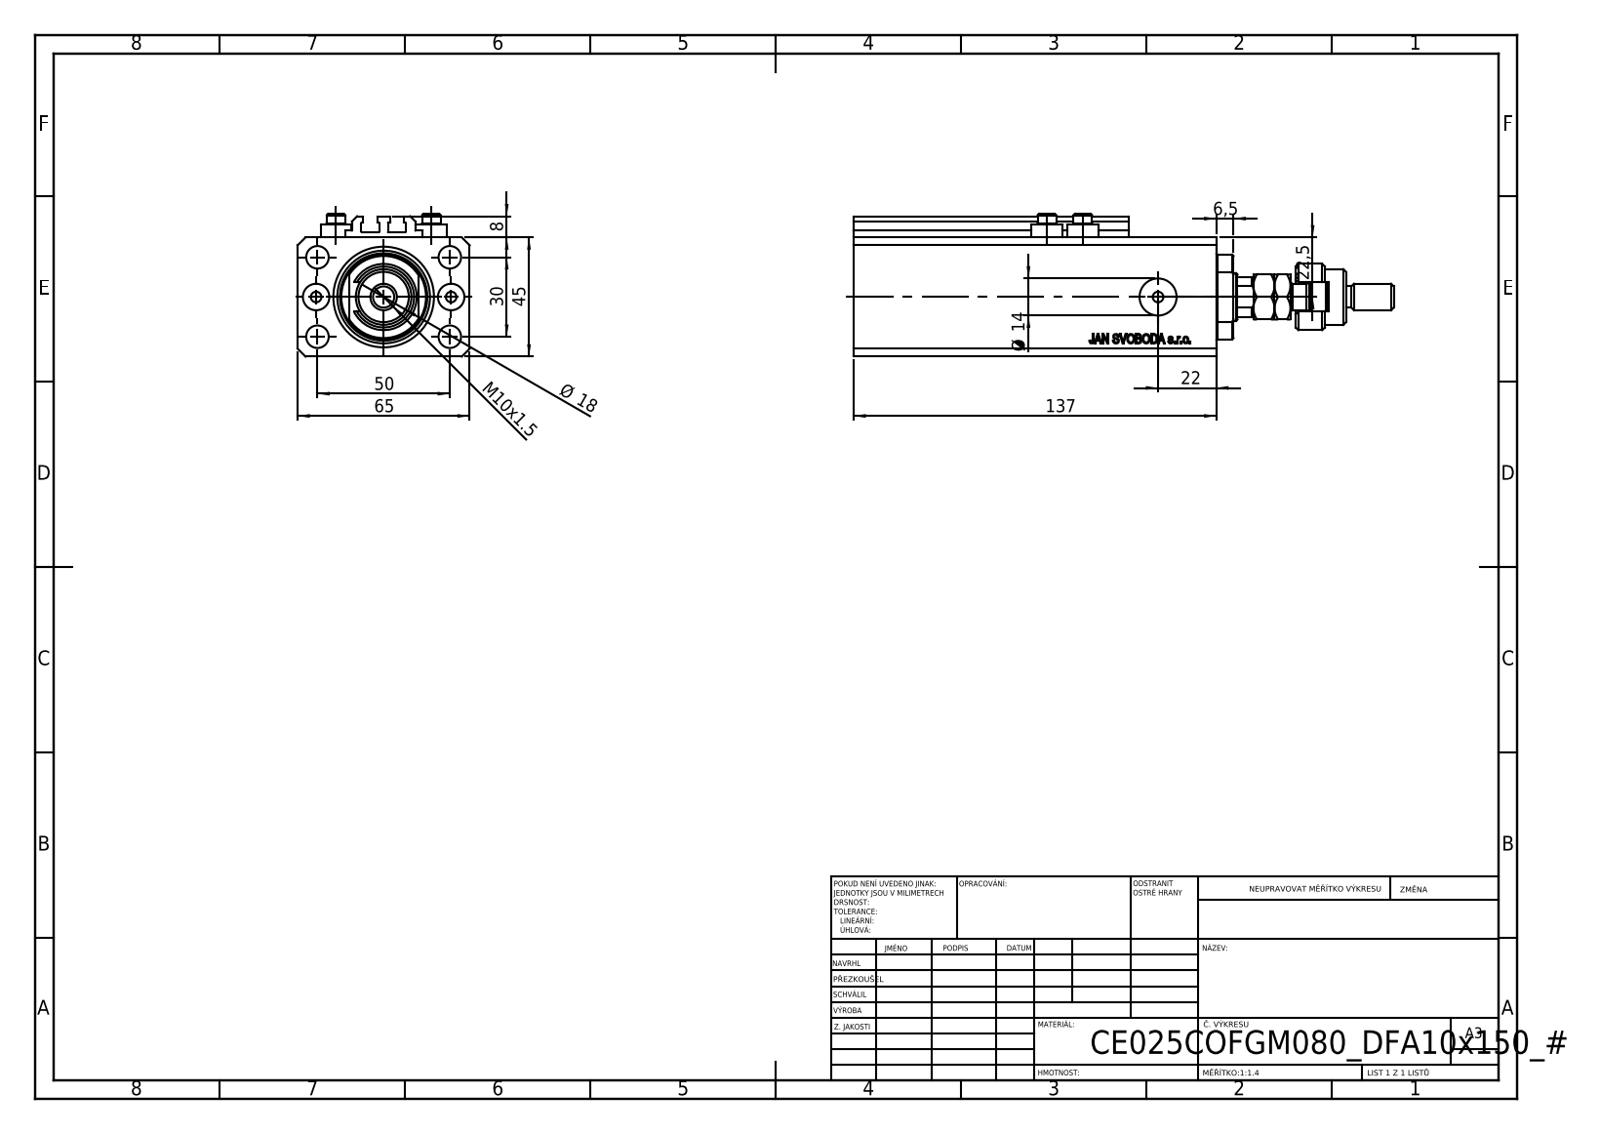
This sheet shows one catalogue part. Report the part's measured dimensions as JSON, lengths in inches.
{"part_name": "MFA; ALLEN BOLT V250CE; V250CE_C_VCP; V250CE_C_Body (+2 more)", "step_written_by": "SolidWorks 2019 (CONFIG_CONTROL_DESIGN)", "units": "inches", "bodies": {"solids": 10, "faces": 1119, "planar": 532, "cylindrical": 99, "other": 488}, "overall_size": [8.031, 2.559, 2.126], "volume_in3": 23.06, "surface_area_in2": 148.9, "round_holes": [[0.157, 8], [0.335, 5], [0.394, 2], [0.551, 2], [0.709, 1], [1.496, 1]], "round_bosses_or_shafts": [[0.457, 4], [0.276, 4], [0.984, 1], [0.827, 1], [0.63, 1], [0.394, 1], [0.315, 1]], "partial_cylinders_radius": [[0.008, 10], [0.217, 1], [0.335, 1], [0.344, 1], [0.63, 1]], "face_to_face_distances": [1.772, 2.559, 0.551, 1.85, 0.079, 4.843, 5.394, 0.098, 0.394, 0.807], "hole_center_spacings": [0.591, 1.148, 2.074, 0.535, 1.004, 1.181, 1.417, 1.515]}
